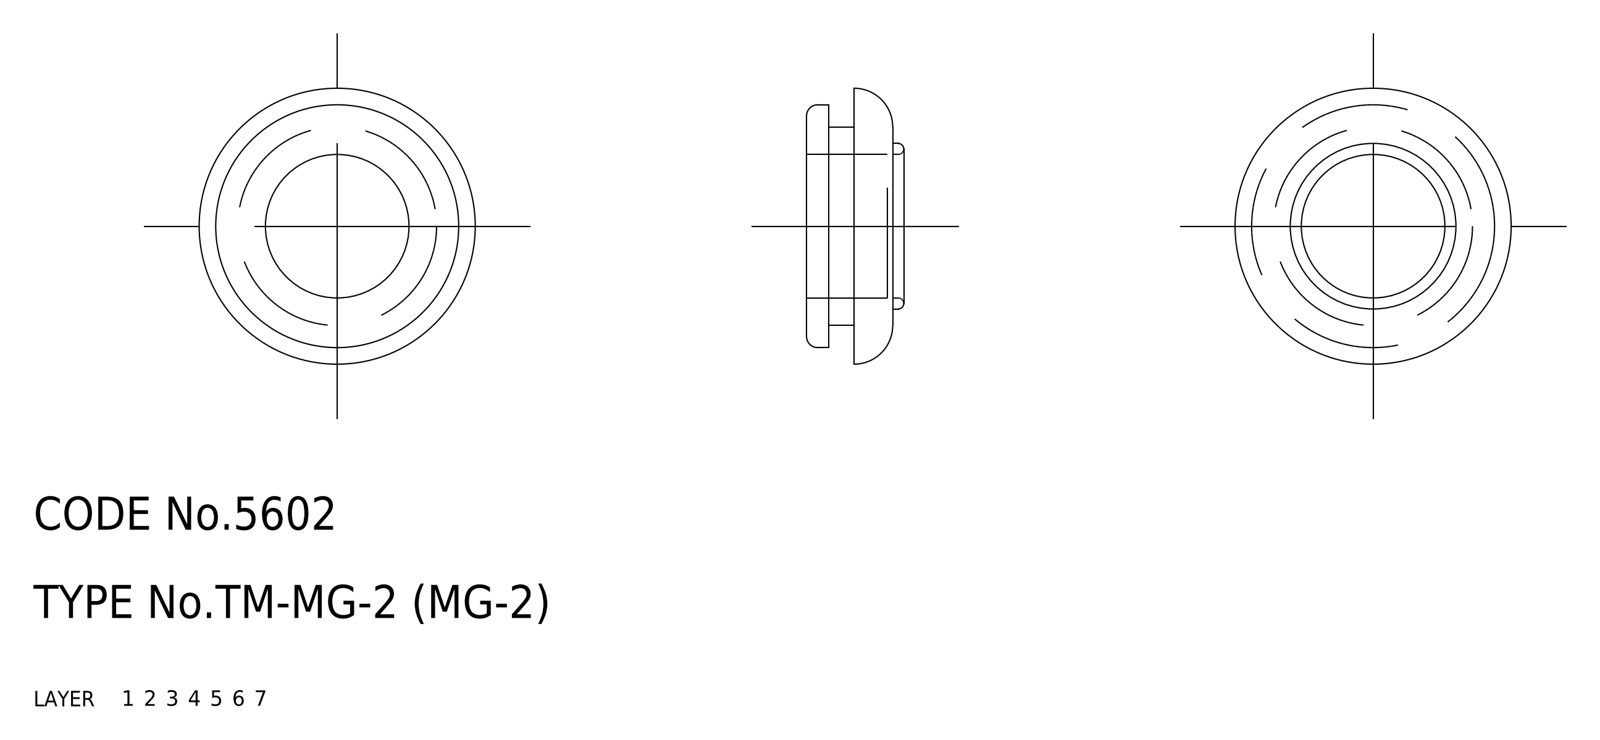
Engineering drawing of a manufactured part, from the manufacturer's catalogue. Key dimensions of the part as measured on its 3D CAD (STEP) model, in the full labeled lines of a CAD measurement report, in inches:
Part name (STEP PRODUCT): grommet
STEP written by: CADfix (AUTOMOTIVE_DESIGN)
Units: inches
Bodies: 1 solid, 22 faces (0 planar, 0 cylindrical, 22 other)
Overall size (bounding box): 0.984 × 0.984 × 0.346
Volume: 0.118 in³ · Surface area: 3.086 in²
